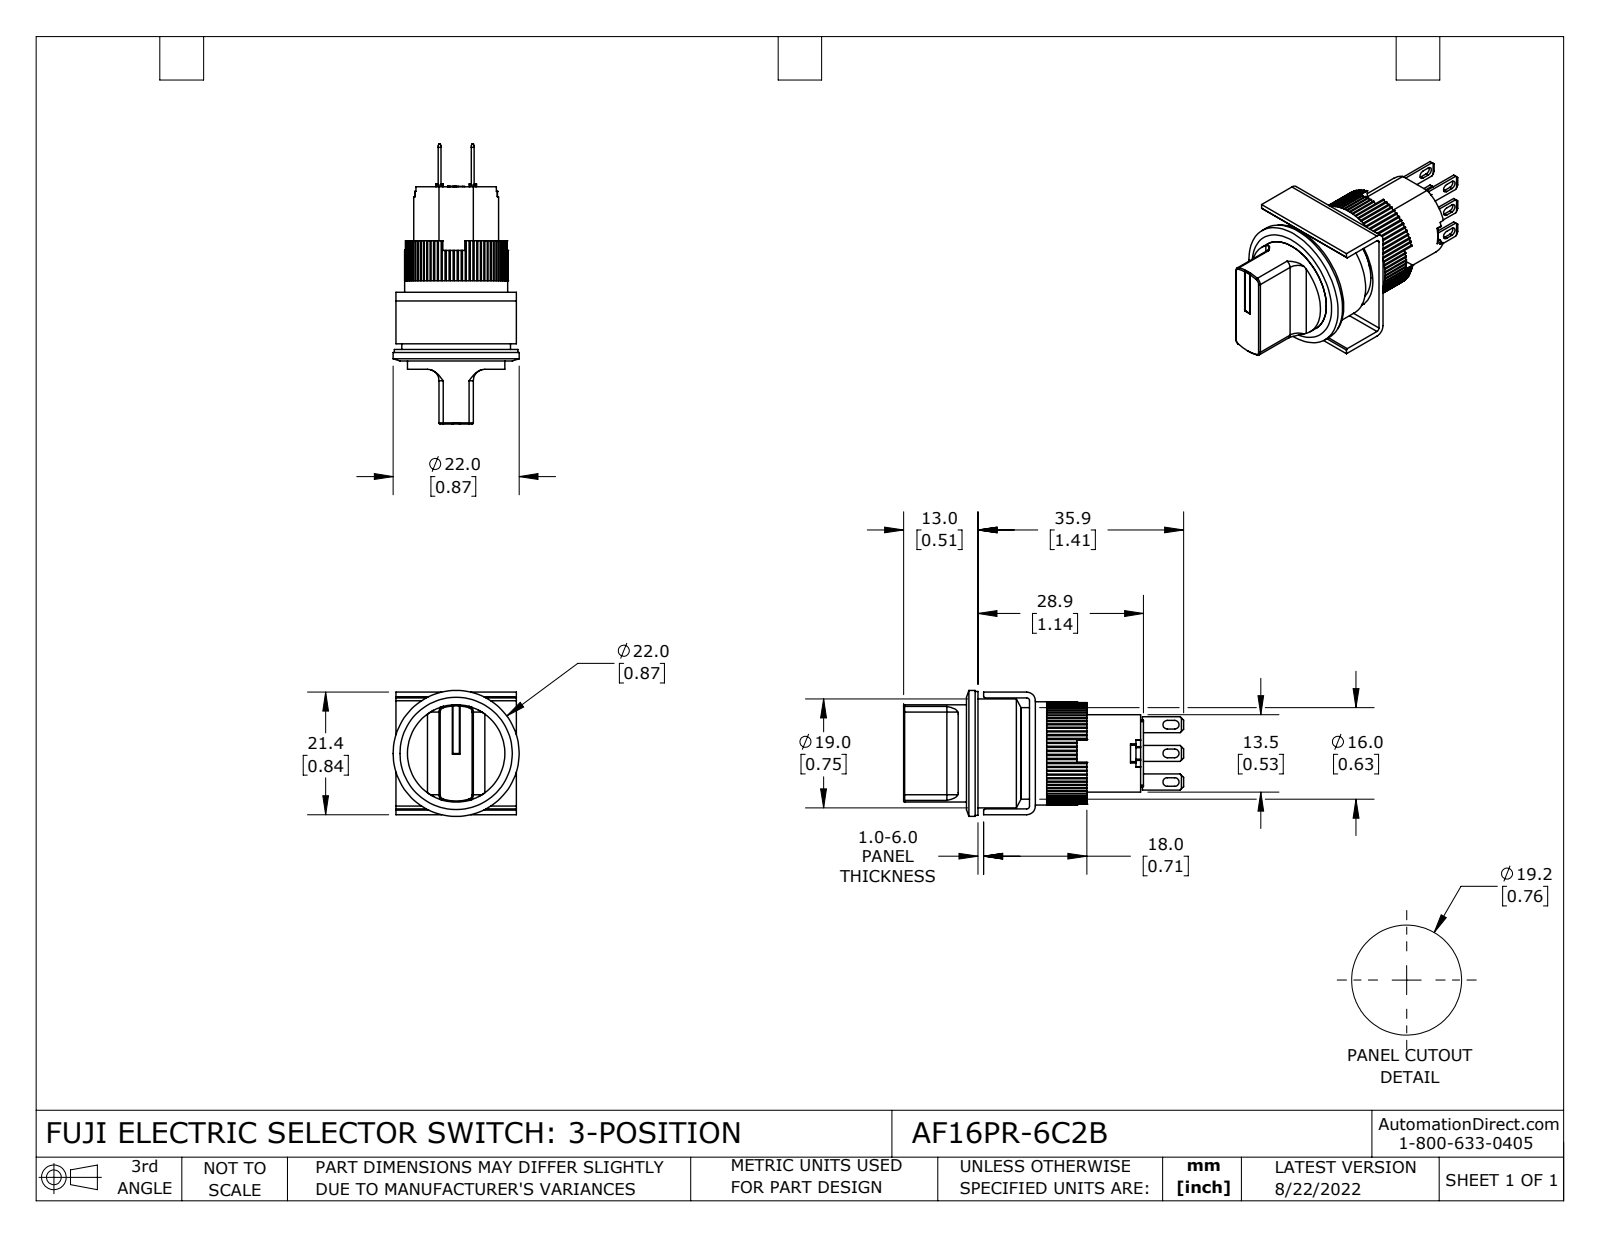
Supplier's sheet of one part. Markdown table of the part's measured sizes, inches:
| quantity | value |
| --- | --- |
| part name | AF16PR-6C2B |
| STEP written by | SolidWorks 2021 (CONFIG_CONTROL_DESIGN) |
| units | inches |
| bodies | 12 solids, 709 faces (505 planar, 189 cylindrical, 15 other) |
| overall size | 1.925 × 0.866 × 0.866 |
| volume | 0.493 in³ |
| surface area | 10.41 in² |
| round holes (diameter × count) | 0.039 × 1, 0.669 × 1, 0.709 × 1, 0.748 × 1 |
| round bosses / shafts (diameter × count) | 0.866 × 1, 0.85 × 1, 0.63 × 1, 0.583 × 1 |
| partial cylindrical surfaces (radius × count) | 0.01 × 80, 0.008 × 14, 0.03 × 6, 0.039 × 4, 0.02 × 2, 0.059 × 2, 0.079 × 2, 0.331 × 1 |
| main face-to-face distances | 0.374, 0.039, 0.059, 0.803, 0.764, 0.02, 0.433, 0.155, 0.648, 0.232 |
